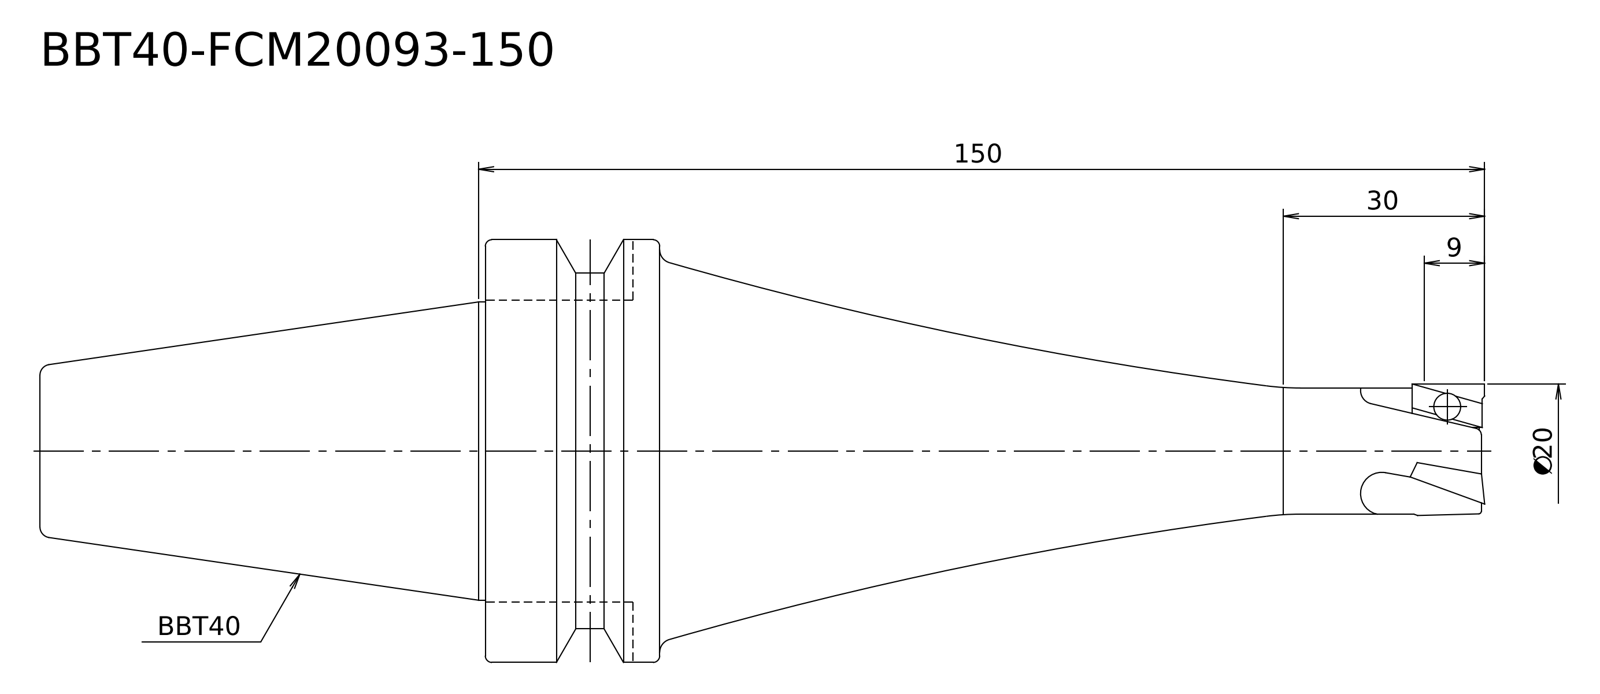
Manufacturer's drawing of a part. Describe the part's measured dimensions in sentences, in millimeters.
Its 3-D file was written by "Kubotek KeyCreator V8.5.1 (14335) (CONFIG_CONTROL_DESIGN)". It is 1 solid with 17 faces: 4 planar, 6 cylindrical and 7 other. Overall it measures 215.4 by 63 by 63 millimeters. Its volume is 261 204 cubic millimeters and its surface area 29 240 square millimeters. Round bosses or shafts: 1 of diameter 63, 1 of diameter 53, 1 of diameter 44.45, 1 of diameter 20, 1 of diameter 18.8. The main face-to-face distances are 66.4, 149, 215.4, 123, 26, 92.4.
